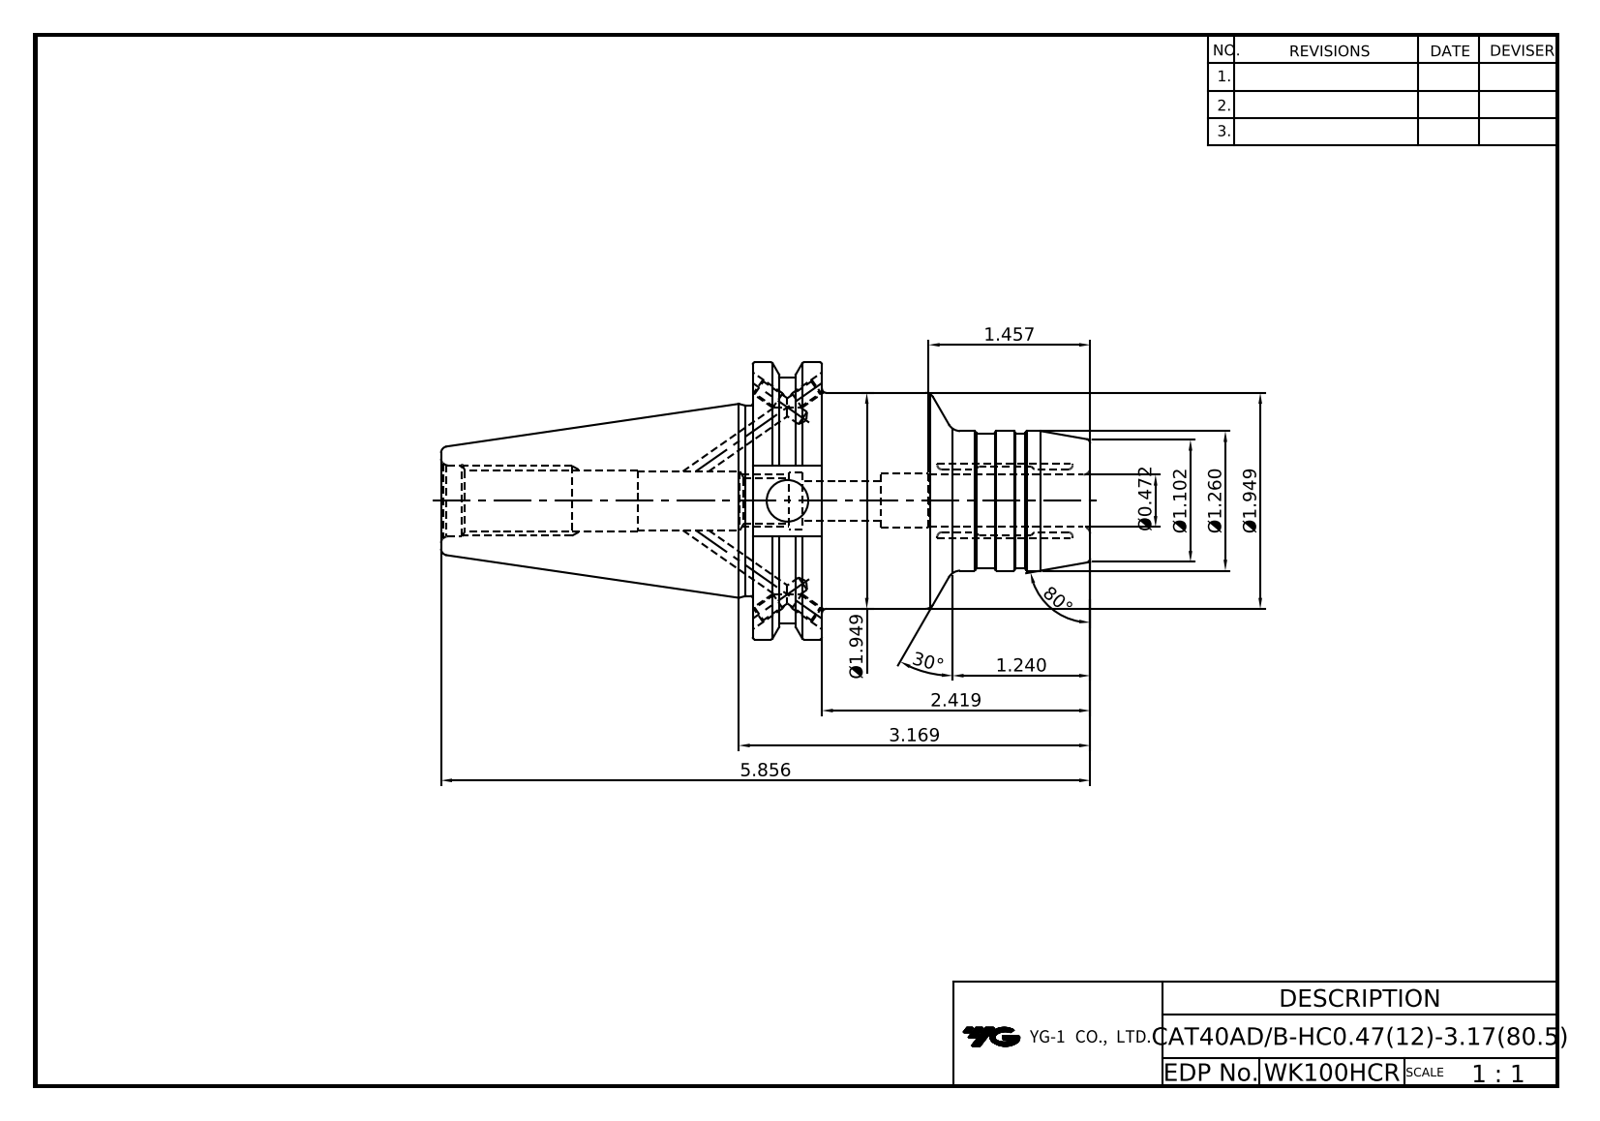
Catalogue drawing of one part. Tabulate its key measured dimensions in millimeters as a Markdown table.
| quantity | value |
| --- | --- |
| part name | LO-CAT40ADB-HCR12-80.5 |
| STEP written by | Autodesk Inventor 2022 (AUTOMOTIVE_DESIGN) |
| units | millimeters |
| bodies | 1 solid, 106 faces (34 planar, 35 cylindrical, 37 other) |
| overall size | 148.75 × 63.5 × 61.09 |
| volume | 173 637 mm³ |
| surface area | 30 156 mm² |
| round holes (diameter × count) | 3.24 × 4, 4 × 4, 9.1 × 1, 9.53 × 1, 10.11 × 1, 12 × 1, 12.6 × 1, 13 × 1, 13.39 × 1, 16.3 × 1 |
| round bosses / shafts (diameter × count) | 63.5 × 1, 56.3 × 1, 49.5 × 1, 43.6 × 1, 32 × 1, 31 × 1 |
| partial cylindrical surfaces (radius × count) | 8.19 × 1 |
| main face-to-face distances | 15.88, 77.33, 61.45, 47.6, 16.38, 71.42, 87.3, 148.75, 77.47, 81.3 |
| hole center spacings | 35.13 |
